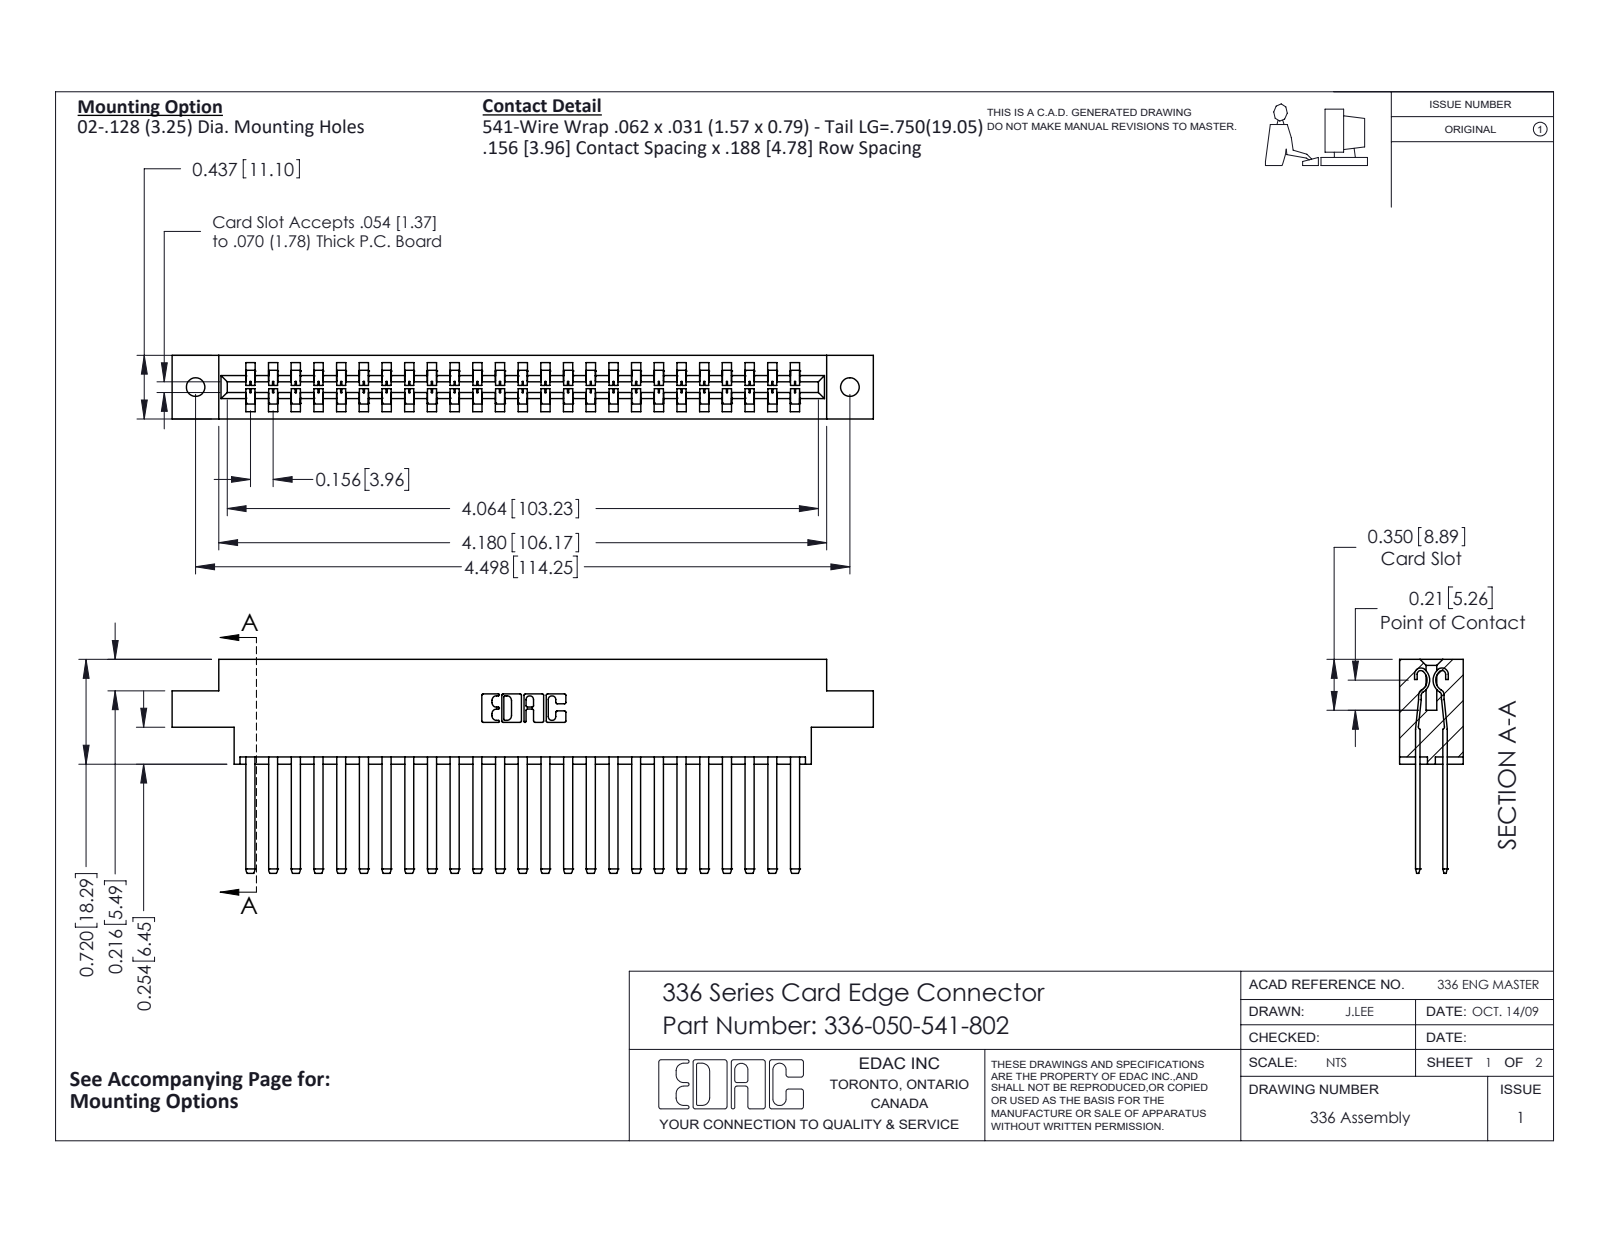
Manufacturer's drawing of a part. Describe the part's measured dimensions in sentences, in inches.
The part is named "336-290-001_336-290-541; 336-050-541-802; 336 Part_Offset - .128 Dia". Its 3-D file was written by "SolidWorks 2020 (CONFIG_CONTROL_DESIGN)". It is 51 solids with 2218 faces: 1374 planar, 844 cylindrical and 0 other. Overall it measures 4.821 by 1.47 by 0.437 inches. Its volume is 1.11 cubic inches and its surface area 35.44 square inches. Round holes: 2 of diameter 0.128. Partial cylindrical surfaces (rounded edges, fillets, slot ends): 100 of radius 0.004, 50 of radius 0.056, 22 of radius 0.01, 6 of radius 0.007, 6 of radius 0.031, 4 of radius 0.022, 4 of radius 0.04, 3 of radius 0.026. The main face-to-face distances are 0.188, 0.328, 0.14, 0.297, 0.109, 0.031, 0.437, 0.033, 0.181, 0.256. The hole center spacings are 4.498.
